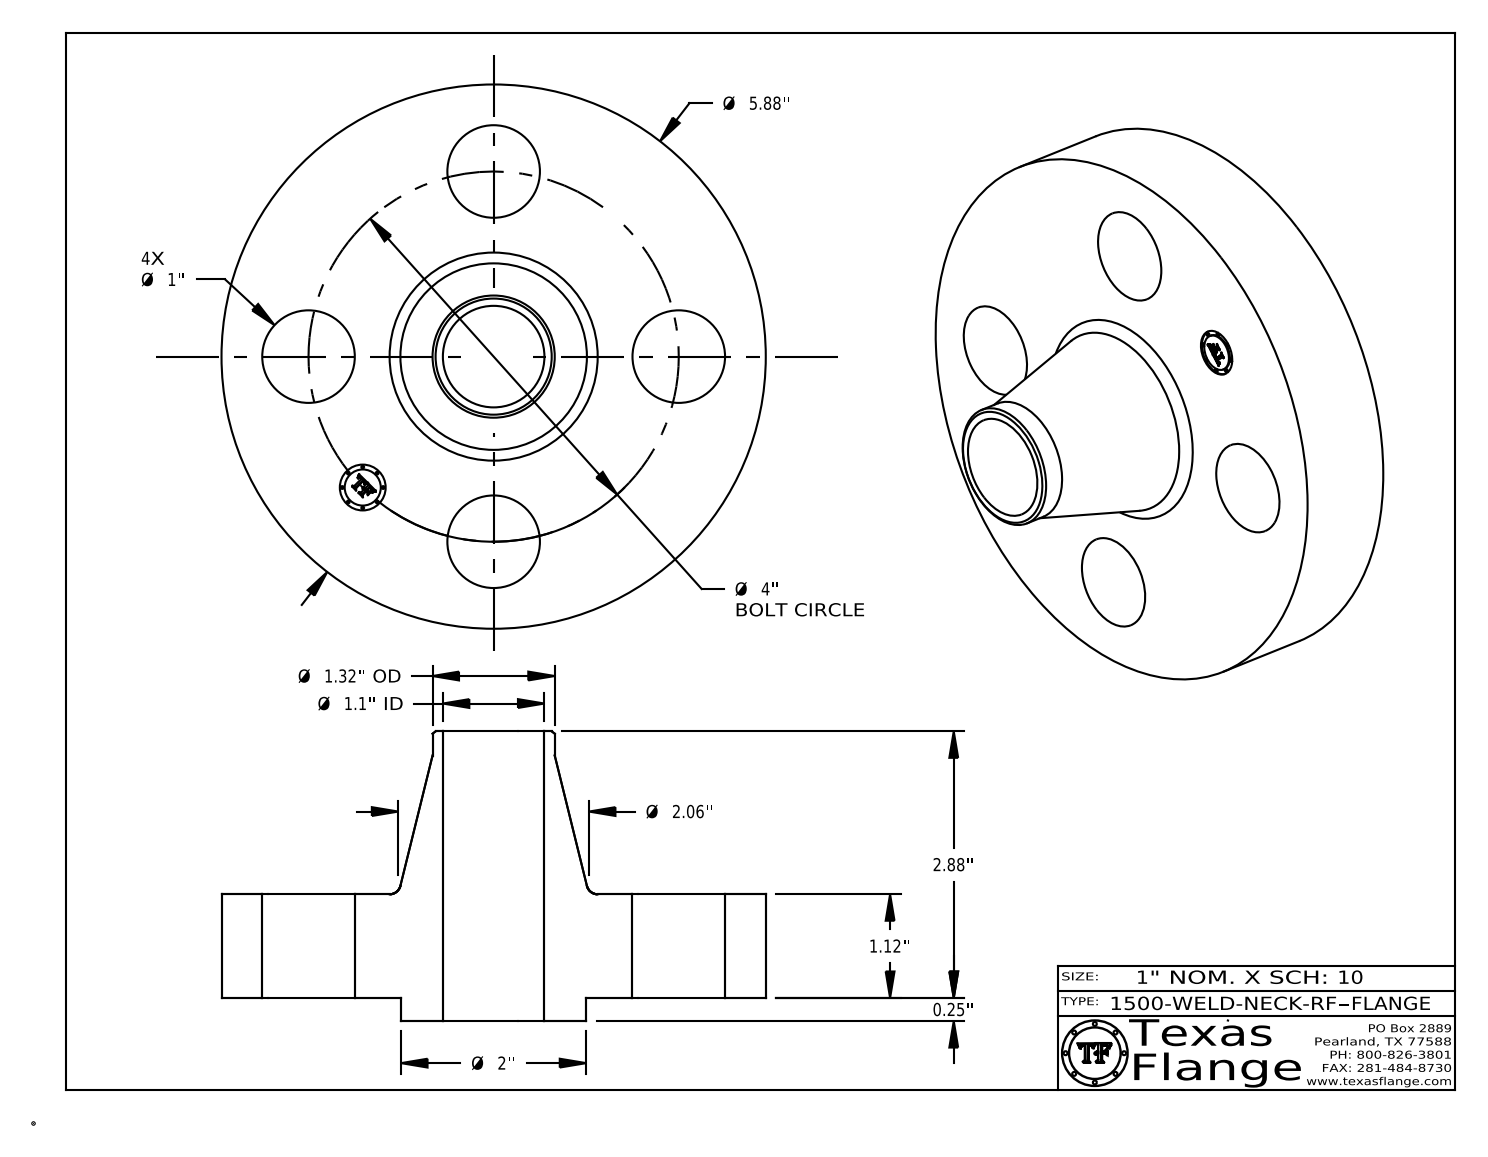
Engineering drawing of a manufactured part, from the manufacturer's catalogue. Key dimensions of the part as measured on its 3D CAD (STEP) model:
Part name (STEP PRODUCT): 1500-WELD-NECK-RF
STEP written by: CATIA V5 STEP AP214 (AUTOMOTIVE_DESIGN)
Units: inches
Bodies: 1 solid, 411 faces (369 planar, 36 cylindrical, 6 other)
Overall size (bounding box): 5.88 × 5.88 × 3.13
Volume: 28.5 in³ · Surface area: 100.4 in²
Round holes (diameter × count): ⌀1 ×4, ⌀0.495 ×1, ⌀1.097 ×1
Round bosses / shafts (diameter × count): ⌀0.03 ×8, ⌀5.88 ×1, ⌀2 ×1, ⌀1.32 ×1, ⌀0.39 ×1
Main face-to-face distances: 1.12, 0.25, 1.37, 3.13, 2.88, 1.76, 0.015, 1.355, 1.105, 1.775
Hole centre spacings: 2, 2.828, 1.531, 3.695, 4
